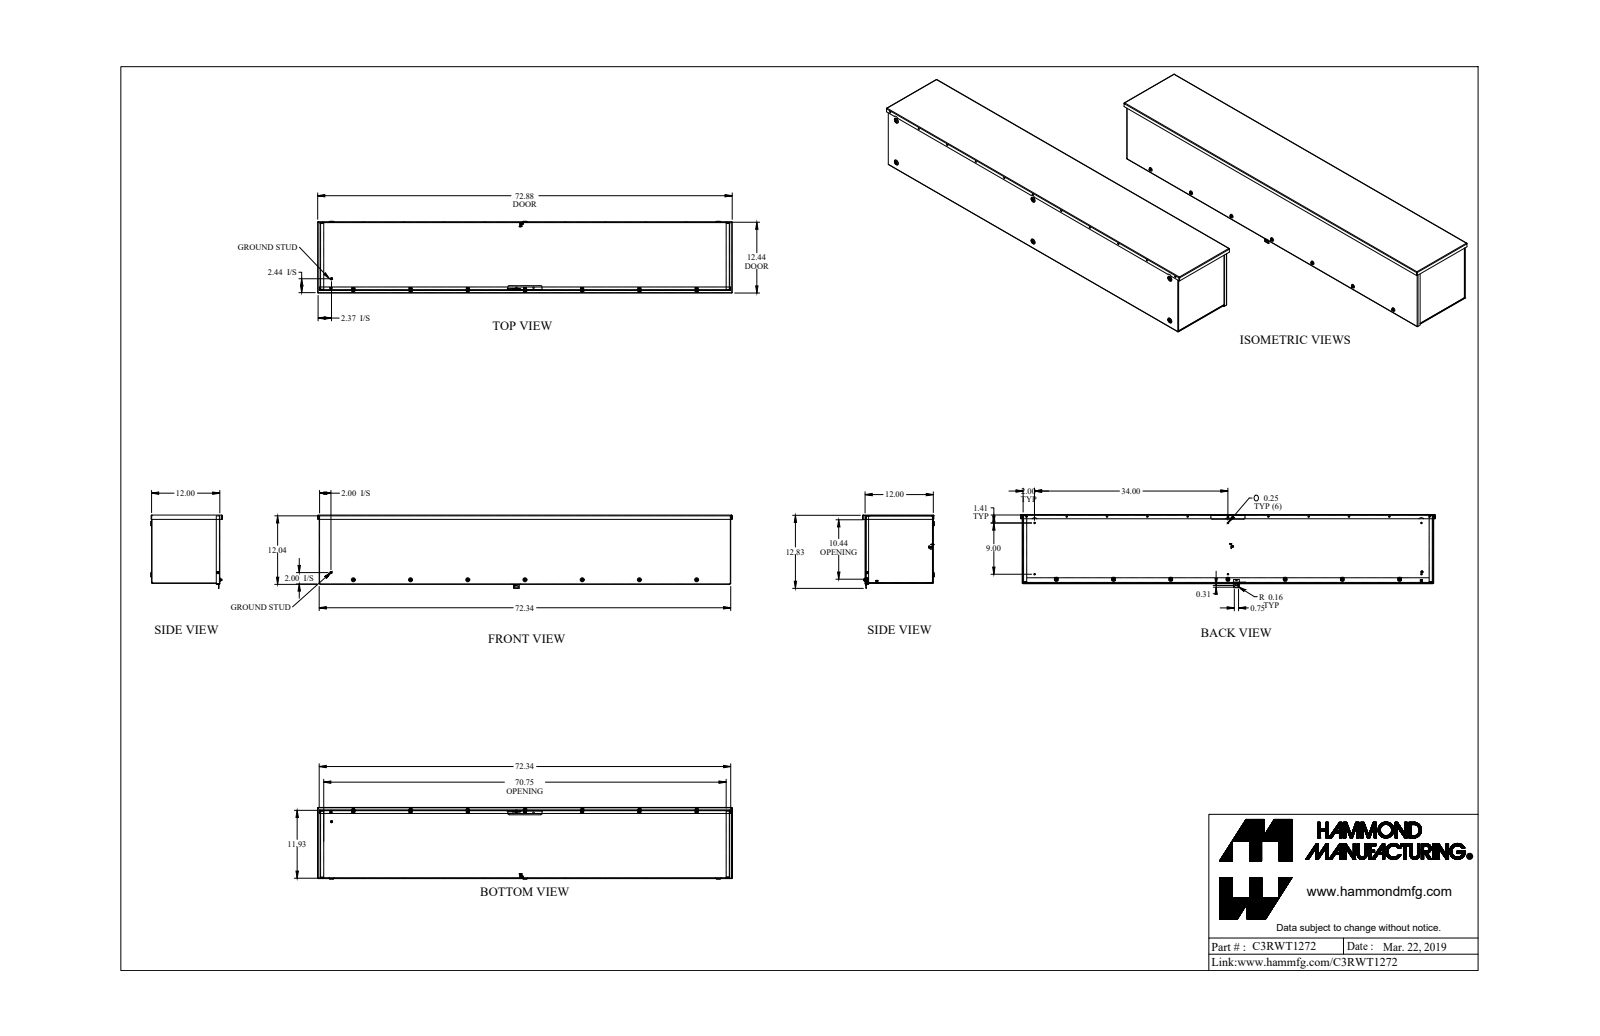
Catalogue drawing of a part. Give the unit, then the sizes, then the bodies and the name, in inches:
Units: inches
Overall size (bounding box): 72.875 × 12.871 × 12.594
Round holes (diameter × count): ⌀0.25 ×19, ⌀0.156 ×9, ⌀0.214 ×7, ⌀0.23 ×7, ⌀0.203 ×2, ⌀0.125 ×1, ⌀0.137 ×1, ⌀0.2 ×1, ⌀0.215 ×1
Round bosses / shafts (diameter × count): ⌀0.19 ×8, ⌀0.148 ×7, ⌀0.375 ×2, ⌀0.5 ×1, ⌀0.367 ×1, ⌀0.21 ×1, ⌀0.152 ×1, ⌀0.125 ×1
Partial cylindrical surfaces — rounded edges, fillets, slot ends (radius × count): R0.08 ×28, R0.108 ×28, R0.036 ×18, R0.108 ×18, R0.125 ×15, R0.022 ×14, R0.171 ×7, R0.206 ×7
Main face-to-face distances: 0.072, 11.928, 12, 11.856, 0.072, 11.856, 11.928, 71.928, 72, 71.856
Hole centre spacings: 7.087, 21.263, 28.35, 14.175, 10.057, 14.175, 20.115, 30.172
Volume: 291.9 in³ · Surface area: 8 172 in²
Bodies: 35 solids, 1321 faces (712 planar, 421 cylindrical, 188 other)
Part name (STEP PRODUCT): C3RWT1272_Default
STEP written by: SolidWorks 2019 (CONFIG_CONTROL_DESIGN)
